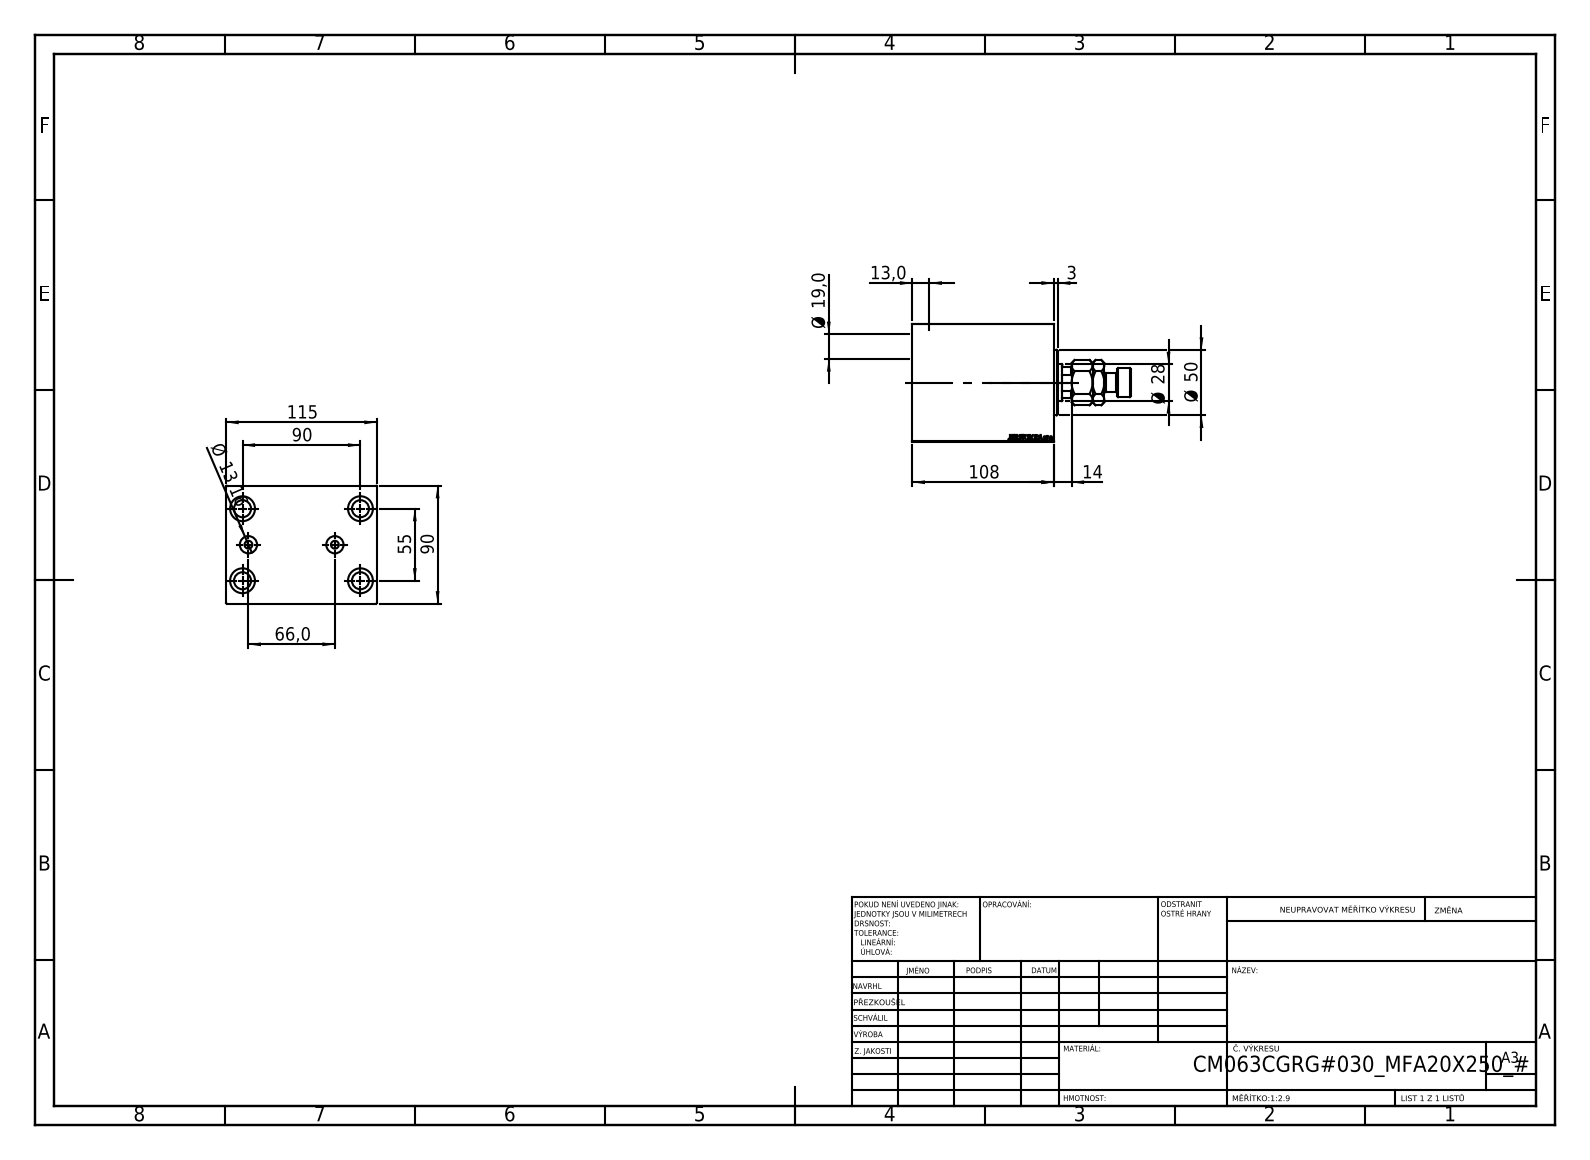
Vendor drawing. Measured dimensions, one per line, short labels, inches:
name: V450CM_VC_B; V450CM_C_Body; V450CM_C_VCP; MFA
written by: SolidWorks 2019 (CONFIG_CONTROL_DESIGN)
unit: in
bodies: 4 solids, 912 faces (424 planar, 62 cylindrical, 426 other)
size: 6.555 × 4.528 × 3.543
volume: 60.58 in³; area: 222.2 in²
holes: 4× ⌀0.512, 4× ⌀0.748, 2× ⌀0.236, 2× ⌀0.518, 1× ⌀0.728, 1× ⌀1.102, 1× ⌀1.24, 1× ⌀2.48, 1× ⌀2.559, 1× ⌀2.835
bosses: 1× ⌀1.969, 1× ⌀0.866, 1× ⌀0.551
rounds: 1× R0.531
face distances: 3.543, 4.528, 4.252, 0.689, 3.563, 0.531, 1.181, 1.713, 3.031, 3.72
hole spacings: 2.076, 1.097, 1.327, 2.165, 2.979, 3.536, 3.543, 4.153
